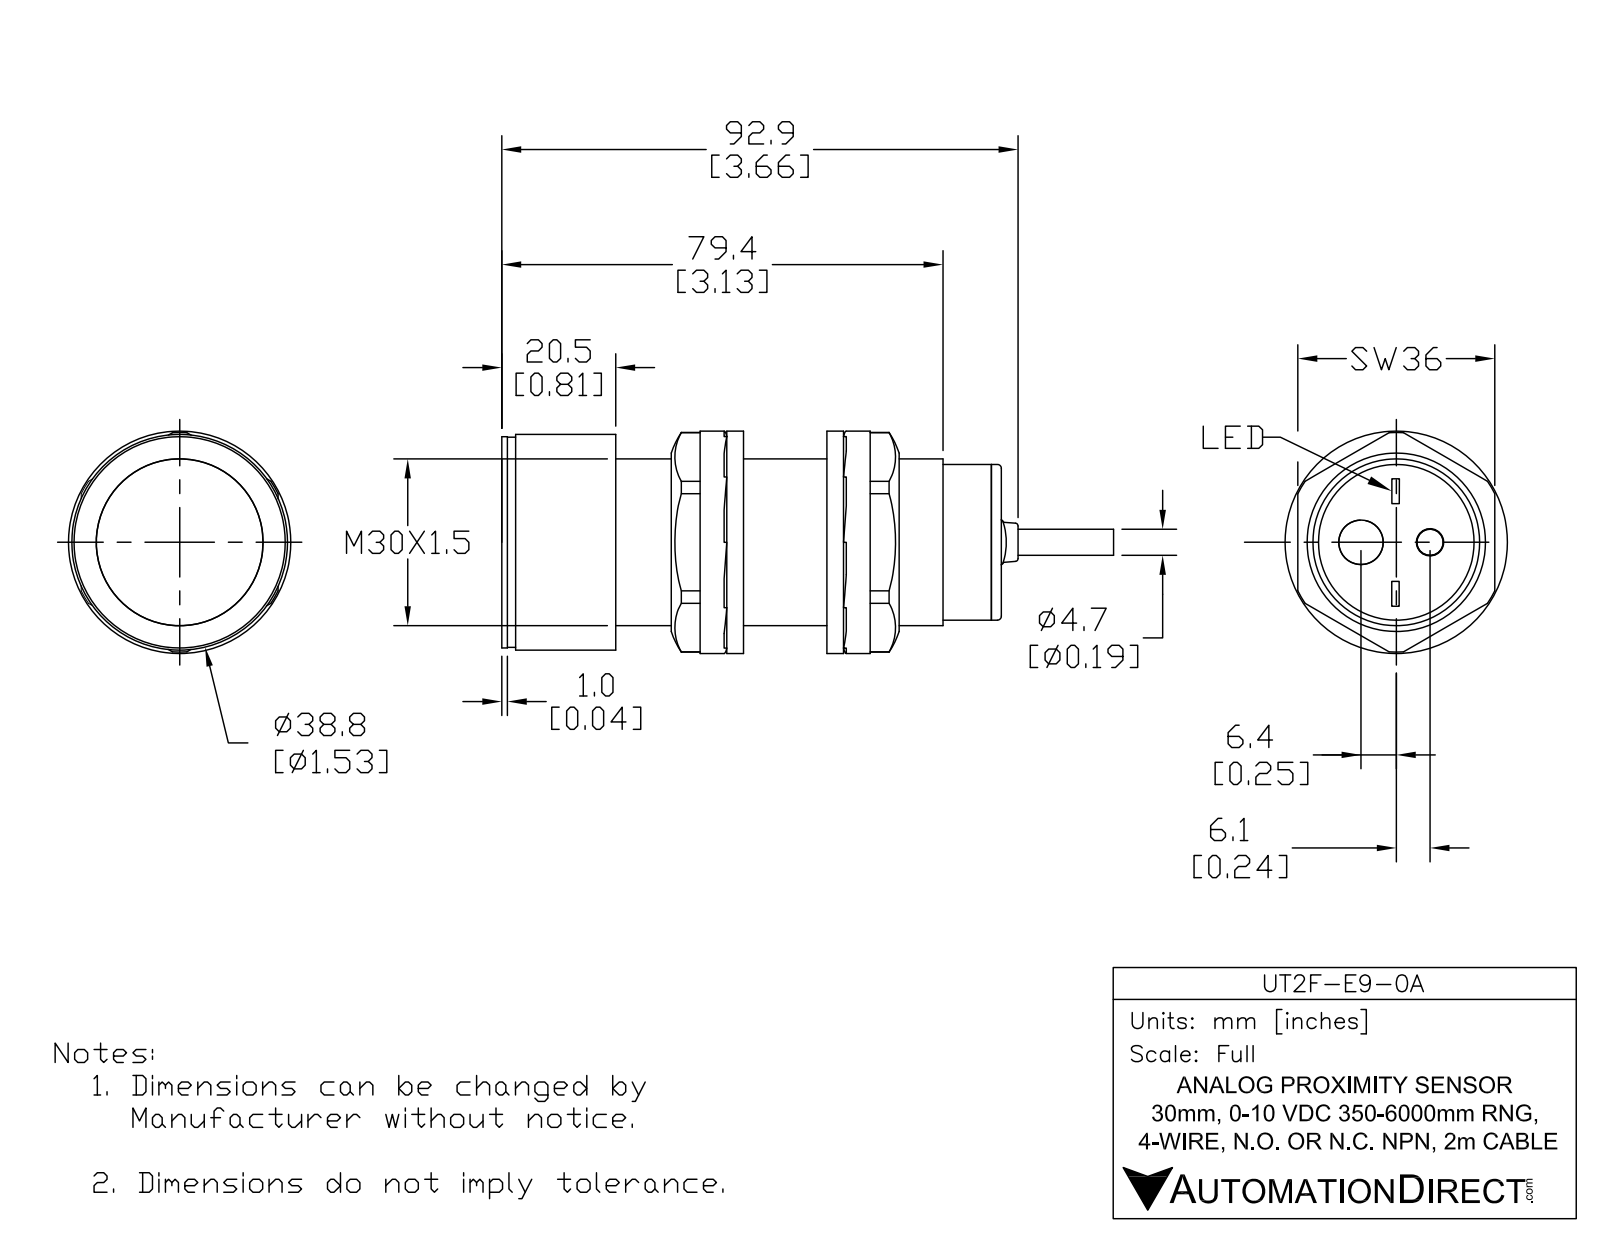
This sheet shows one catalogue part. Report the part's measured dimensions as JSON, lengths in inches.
{"part_name": "UT2F-E9-0A", "step_written_by": "SolidWorks 2017 (AUTOMOTIVE_DESIGN)", "units": "inches", "bodies": {"solids": 5, "faces": 49, "planar": 14, "cylindrical": 20, "other": 15}, "overall_size": [5.043, 1.528, 1.528], "volume_in3": 4.38, "surface_area_in2": 24.02, "round_holes": [[0.185, 1], [0.315, 1], [1.299, 1]], "round_bosses_or_shafts": [[1.528, 1], [1.488, 1], [1.181, 1], [1.102, 1]], "face_to_face_distances": [3.37, 0.059, 3.429, 0.767, 0.709, 2.661, 3.5, 3.441, 2.732, 0.071], "hole_center_spacings": [0.239, 0.25, 0.49]}
